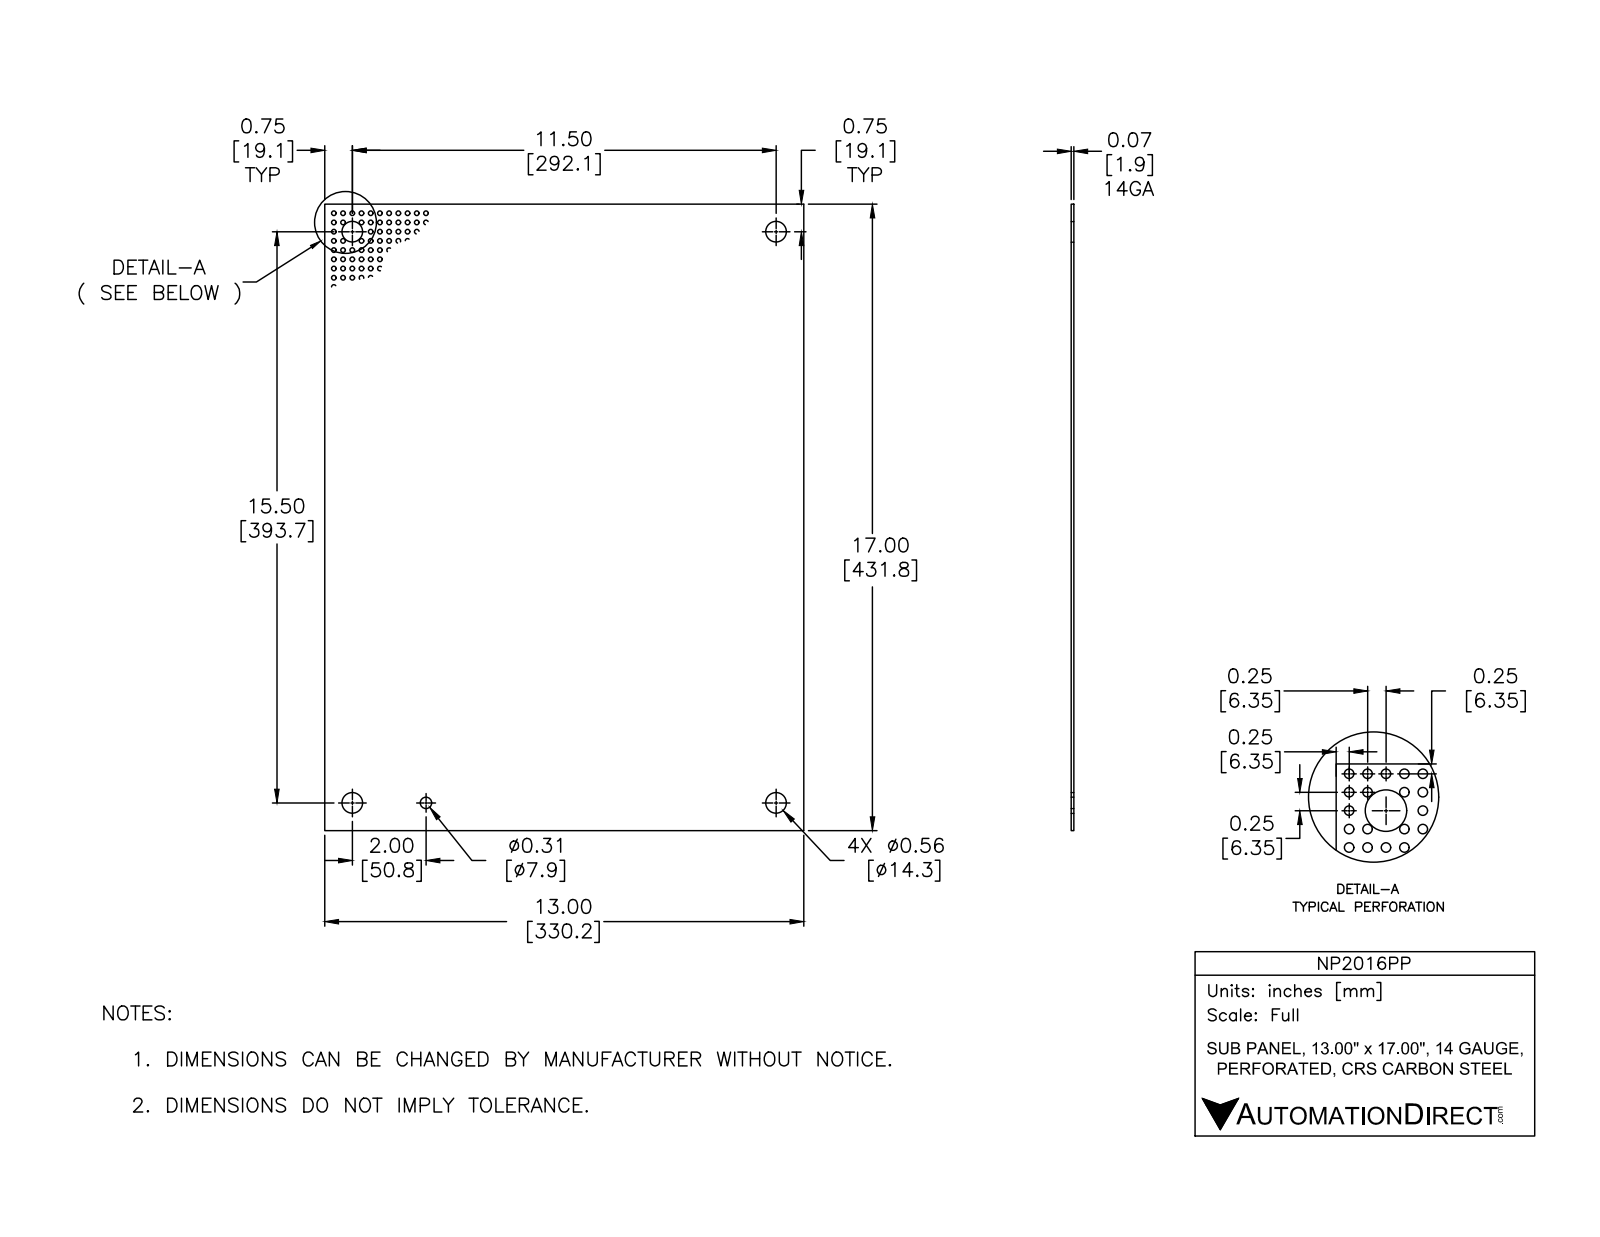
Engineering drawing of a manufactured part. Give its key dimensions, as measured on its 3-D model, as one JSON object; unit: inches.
{"part_name": "NP2016PP", "step_written_by": "Autodesk Inventor 2012 (AUTOMOTIVE_DESIGN)", "units": "inches", "bodies": {"solids": 1, "faces": 11, "planar": 6, "cylindrical": 5, "other": 0}, "overall_size": [17, 13, 0.074], "volume_in3": 16.27, "surface_area_in2": 444.9, "round_holes": [[0.563, 4], [0.31, 1]], "face_to_face_distances": [0.074, 13, 17], "hole_center_spacings": [11.25, 2, 9.25, 15.25, 15.25, 15.381, 17.836, 18.951]}
